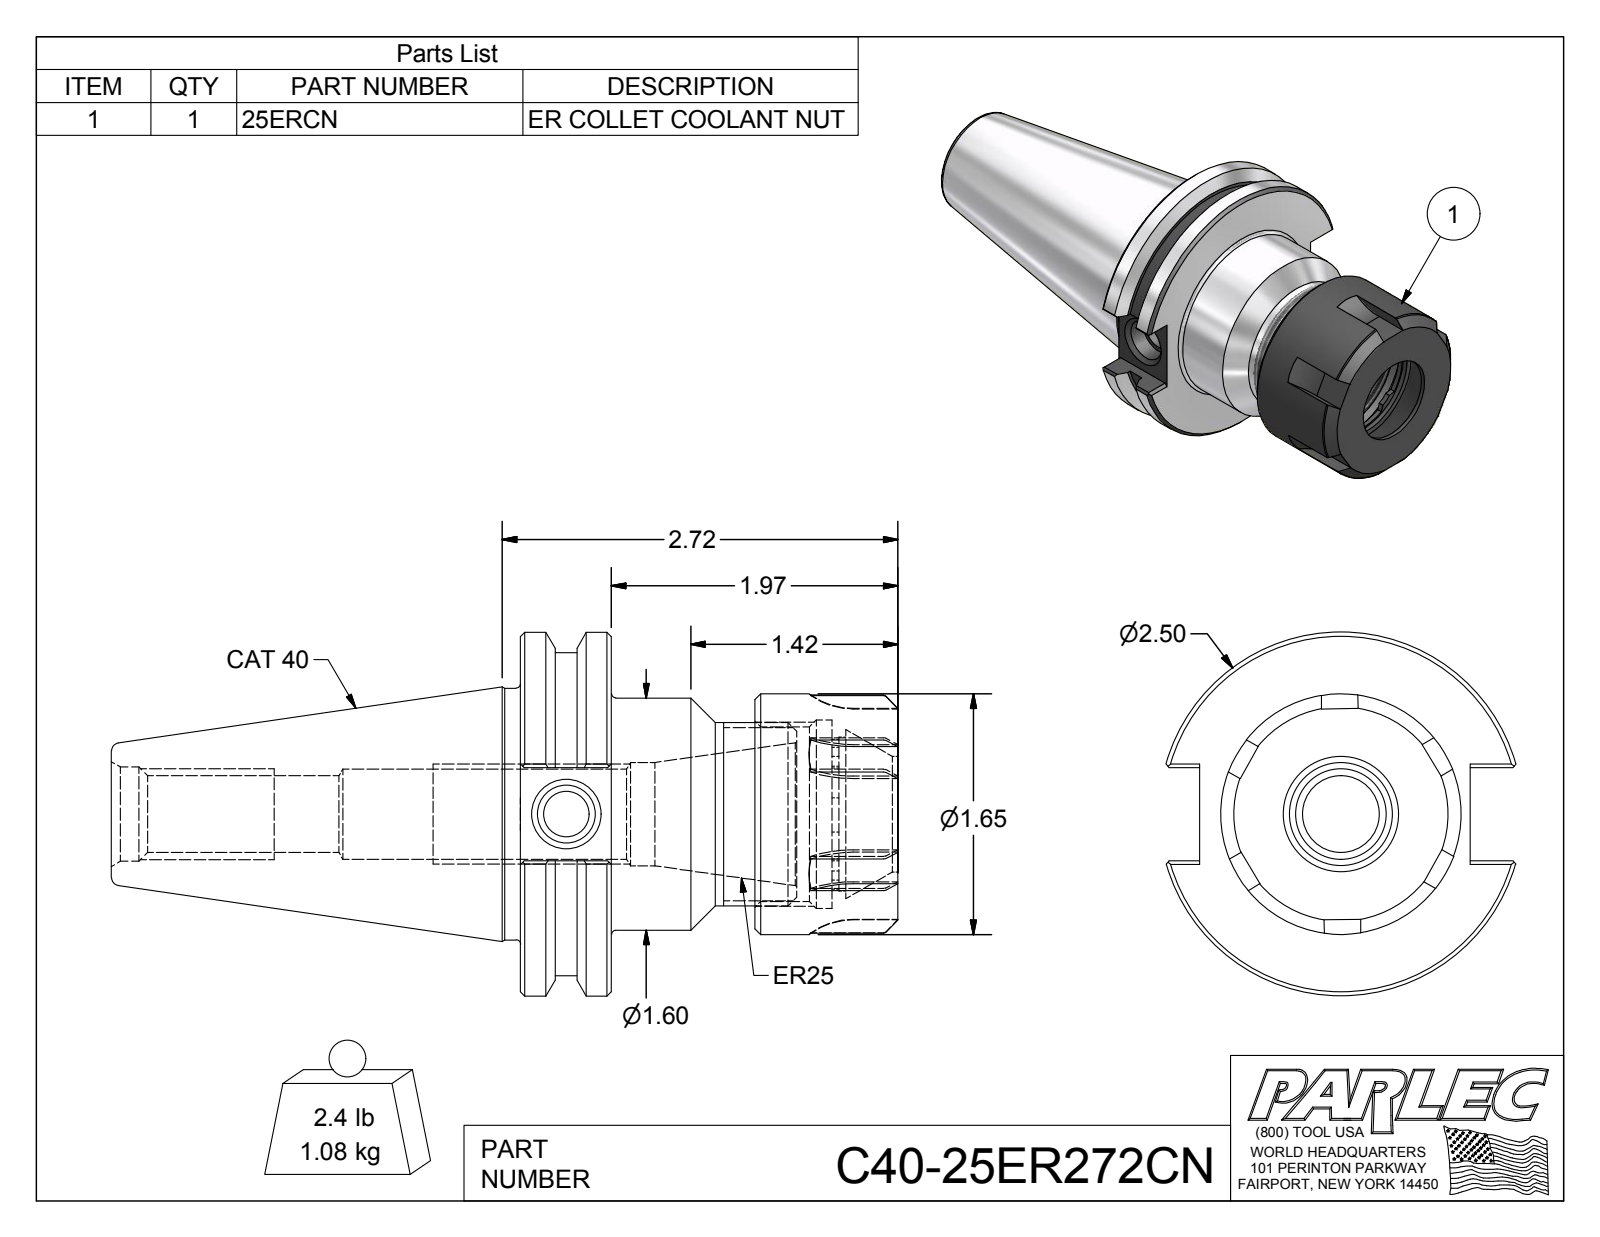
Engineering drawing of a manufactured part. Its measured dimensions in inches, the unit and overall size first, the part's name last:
Units: inches
Overall size (bounding box): 5.408 × 2.5 × 2.403
Round holes (diameter × count): ⌀0.315 ×1, ⌀0.396 ×1, ⌀0.527 ×1, ⌀0.62 ×1, ⌀0.648 ×1, ⌀0.71 ×1, ⌀0.794 ×1, ⌀1.057 ×1, ⌀1.201 ×1, ⌀1.294 ×1
Round bosses / shafts (diameter × count): ⌀2.5 ×1, ⌀2.219 ×1, ⌀1.73 ×1, ⌀1.654 ×1, ⌀1.595 ×1, ⌀1.26 ×1
Partial cylindrical surfaces — rounded edges, fillets, slot ends (radius × count): R0.5 ×6, R0.472 ×1, R0.515 ×1
Main face-to-face distances: 0.625, 2.595, 1.97, 1.611, 0.986, 0.984, 2.142, 1.517, 0.531, 0.453
Volume: 8.407 in³ · Surface area: 51.88 in²
Bodies: 2 solids, 129 faces (59 planar, 31 cylindrical, 39 other)
Part name (STEP PRODUCT): C40-25ER272CN; C40-25ER2-1; 25ERCN
STEP written by: Autodesk Inventor 2012 (AUTOMOTIVE_DESIGN)
